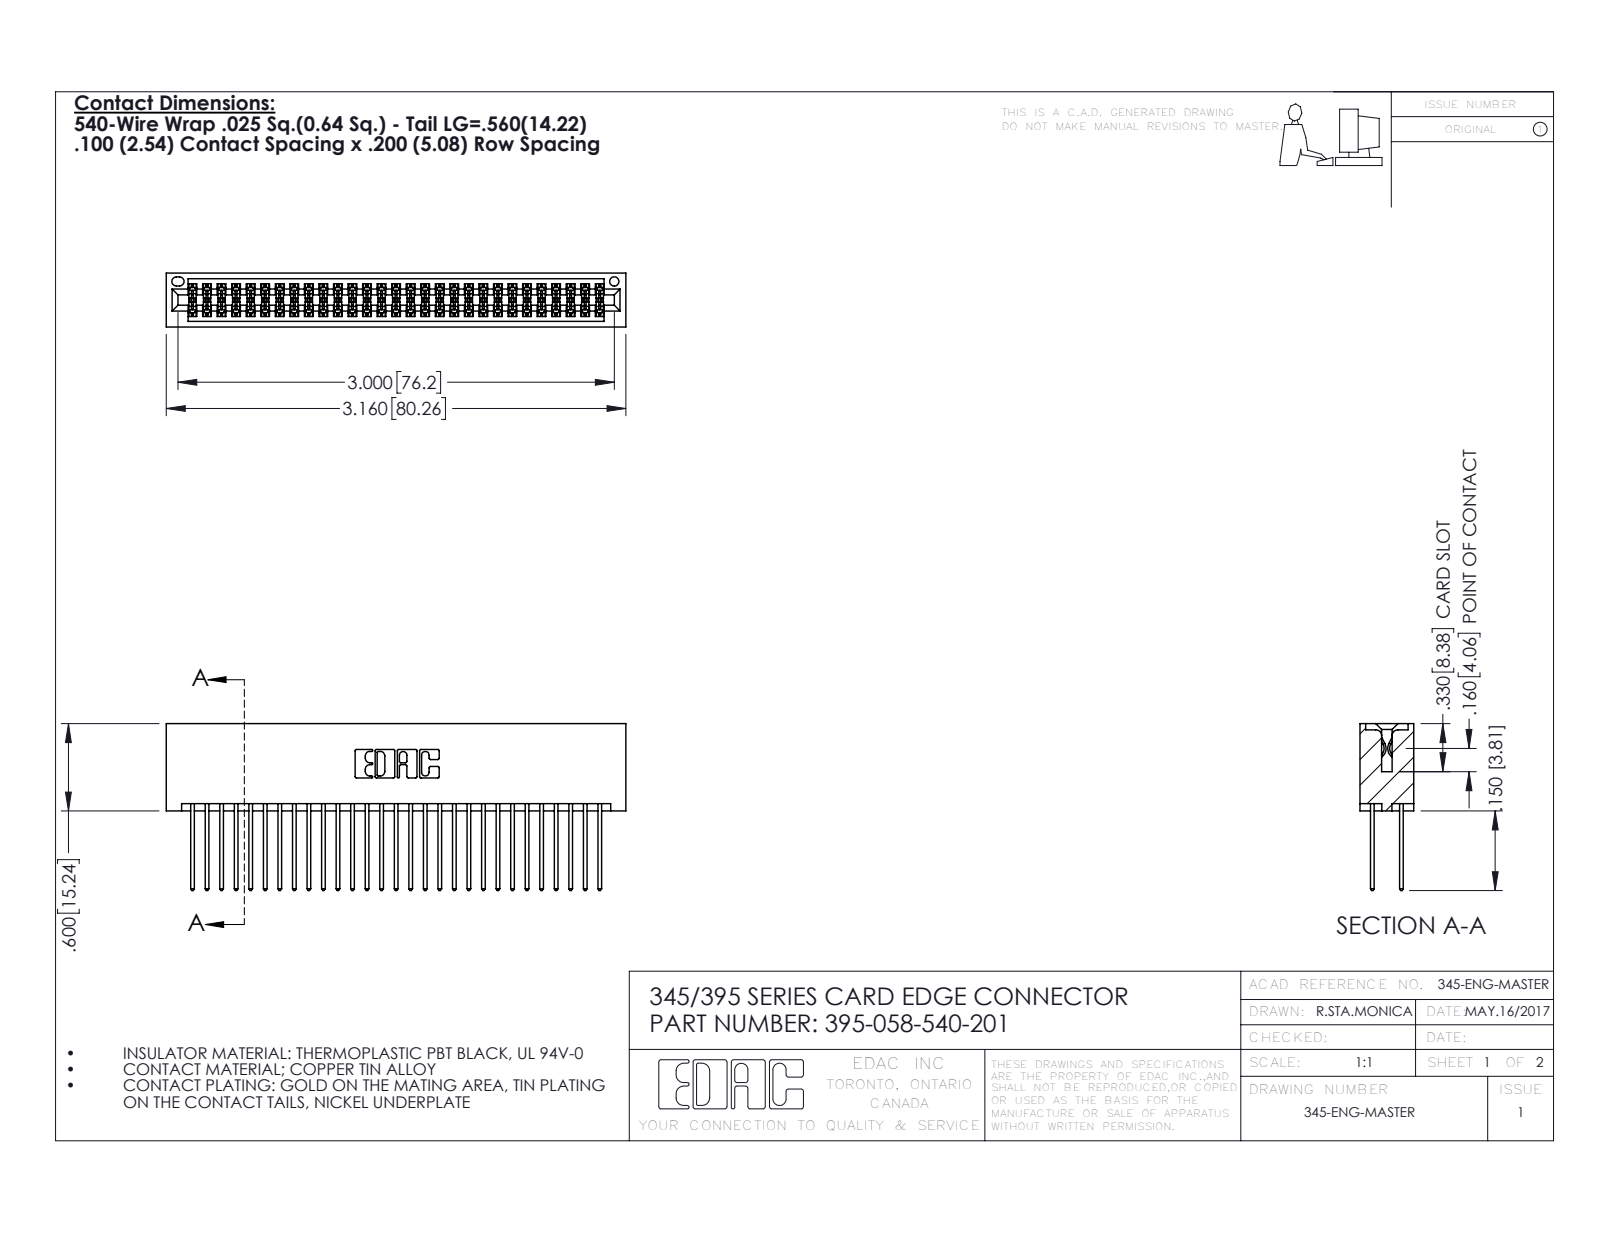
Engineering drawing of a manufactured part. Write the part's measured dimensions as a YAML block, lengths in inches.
part_name: "395-058-540-201; 345-292-001_345-293-140; 345 Part_No Mounting Lugs"
step_written_by: "SolidWorks 2016 (CONFIG_CONTROL_DESIGN)"
units: inches
bodies: {solids: 59, faces: 3018, planar: 1990, cylindrical: 1028, other: 0}
overall_size: [3.16, 1.147, 0.37]
volume: 0.519
surface_area: 21.16
round_holes:
  - {diameter: 0.064, count: 1}
partial_cylinders:
  - {radius: 0.006, count: 87}
  - {radius: 0.01, count: 58}
  - {radius: 0.01, count: 22}
  - {radius: 0.007, count: 6}
  - {radius: 0.031, count: 6}
  - {radius: 0.026, count: 3}
  - {radius: 0.014, count: 2}
  - {radius: 0.019, count: 2}
face_to_face_distances: [0.298, 0.072, 0.2, 0.098, 0.272, 0.025, 0.225, 0.37, 0.175, 0.149]
